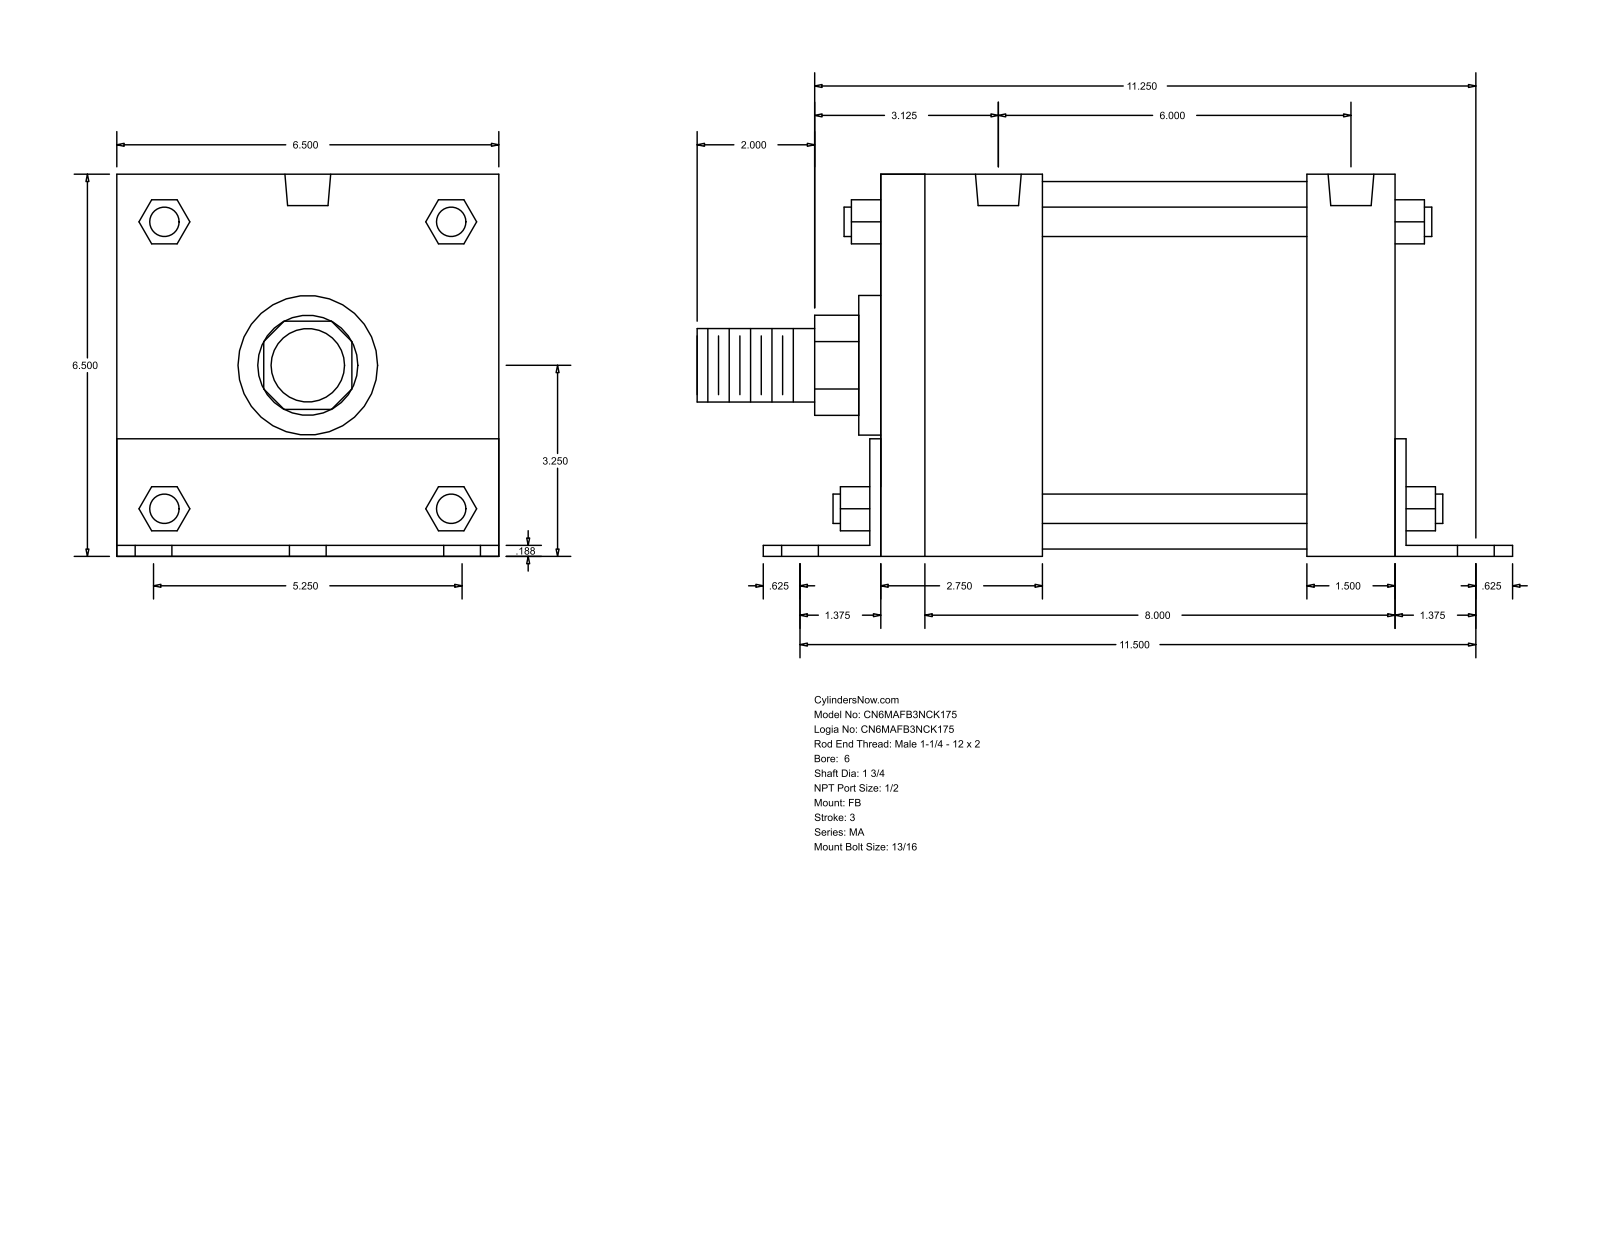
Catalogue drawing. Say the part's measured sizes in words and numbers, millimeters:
The part is named "MA_FB__0600_1.75". Its 3-D file was written by "GSSL Pune (CONFIG_CONTROL_DESIGN)". It is 0 solids with 140 faces: 105 planar, 35 cylindrical and 0 other. Overall it measures 352.43 by 165.15 by 165.1 millimeters. Round holes: 6 of diameter 20.64, 4 of diameter 17.46, 2 of diameter 19.77. Round bosses or shafts: 4 of diameter 12.7, 1 of diameter 158.75, 1 of diameter 60.33, 1 of diameter 44.45, 1 of diameter 31.75. Partial cylindrical surfaces (rounded edges, fillets, slot ends): 1 of radius 21.63, 1 of radius 32.05. The main face-to-face distances are 165.1, 4.76, 222.25, 165.15, 4.71, 160.39, 38.1, 69.85, 74.61, 4.77. The hole center spacings are 66.67, 299.61, 292.1, 85.78, 108.6, 133.34, 152.4, 216.87.
